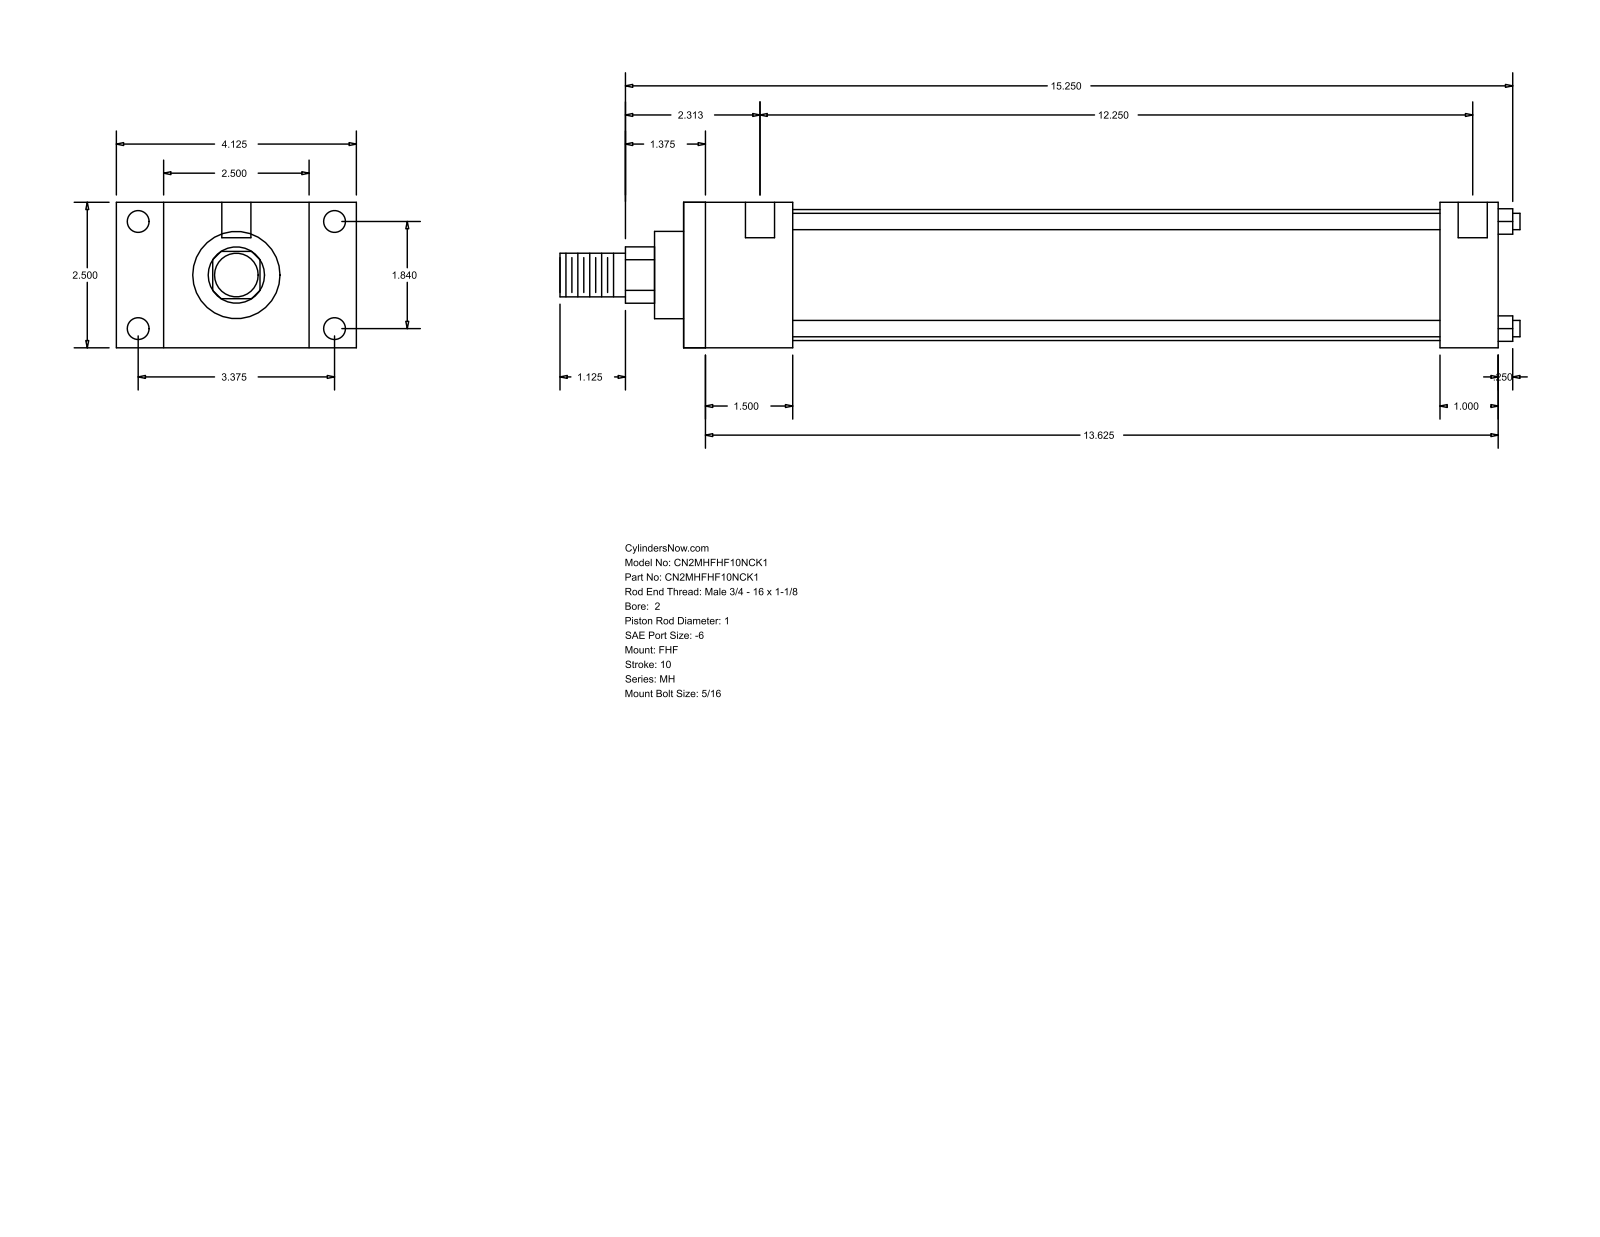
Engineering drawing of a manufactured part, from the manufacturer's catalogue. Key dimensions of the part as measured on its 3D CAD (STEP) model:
Part name (STEP PRODUCT): MH_FHF__0200_1
STEP written by: GSSL Pune (CONFIG_CONTROL_DESIGN)
Units: millimetres
Bodies: 0 solids, 88 faces (60 planar, 28 cylindrical, 0 other)
Overall size (bounding box): 419.1 × 104.78 × 63.5
Round holes (diameter × count): ⌀5.56 ×4, ⌀9.53 ×4, ⌀12.7 ×2
Round bosses / shafts (diameter × count): ⌀7.14 ×4, ⌀57.15 ×1, ⌀38.1 ×1, ⌀25.4 ×1, ⌀19.05 ×1
Partial cylindrical surfaces — rounded edges, fillets, slot ends (radius × count): R12.29 ×1
Main face-to-face distances: 63.5, 355.6, 47.63, 307.97, 20.64, 84.14, 104.78, 25.4, 330.2, 282.57
Hole centre spacings: 46.74, 85.72, 97.63, 319.08, 3.17, 4.76, 311.15, 314.32
